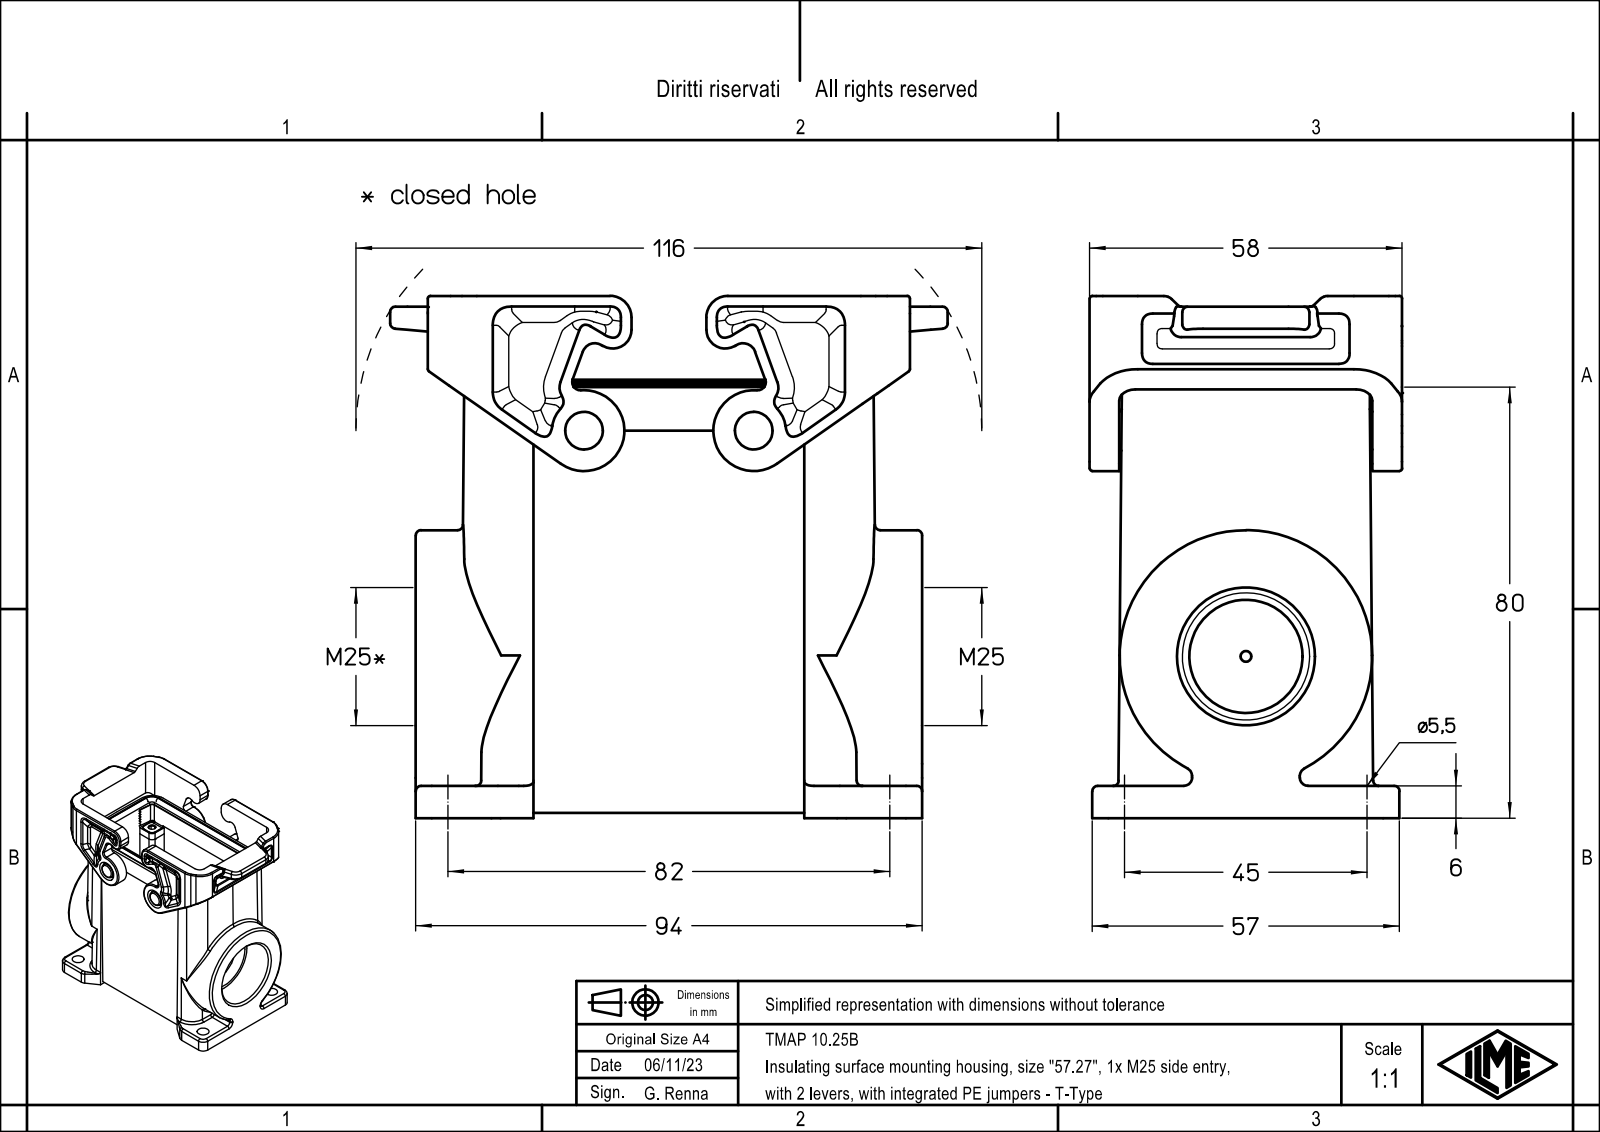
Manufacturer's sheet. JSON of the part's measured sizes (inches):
{"part_name": "TMAP 10.25B", "step_written_by": "Creo Elements/Direct Modeling 20.1B 02-Apr-2019 (C) Parametric Technology GmbH (AUTOMOTIVE_DESIGN)", "units": "inches", "bodies": {"solids": 1, "faces": 606, "planar": 360, "cylindrical": 194, "other": 52}, "overall_size": [4.075, 3.815, 2.283], "volume_in3": 11.28, "surface_area_in2": 98.46, "round_holes": [[0.138, 4], [0.217, 4], [0.827, 1], [0.929, 1]], "round_bosses_or_shafts": [[0.276, 2], [1.845, 1]], "partial_cylinders_radius": [[0.079, 20], [0.118, 20], [0.059, 18], [0.039, 16], [0.051, 12], [0.236, 8], [0.276, 8], [0.157, 6]], "face_to_face_distances": [1.386, 0.217, 0.232, 1.618, 0.039, 0.256, 0.449, 1.835, 2.067, 3.701], "hole_center_spacings": [0.606, 1.5, 2.759, 3.081, 1.063, 1.772, 2.244, 2.483]}
